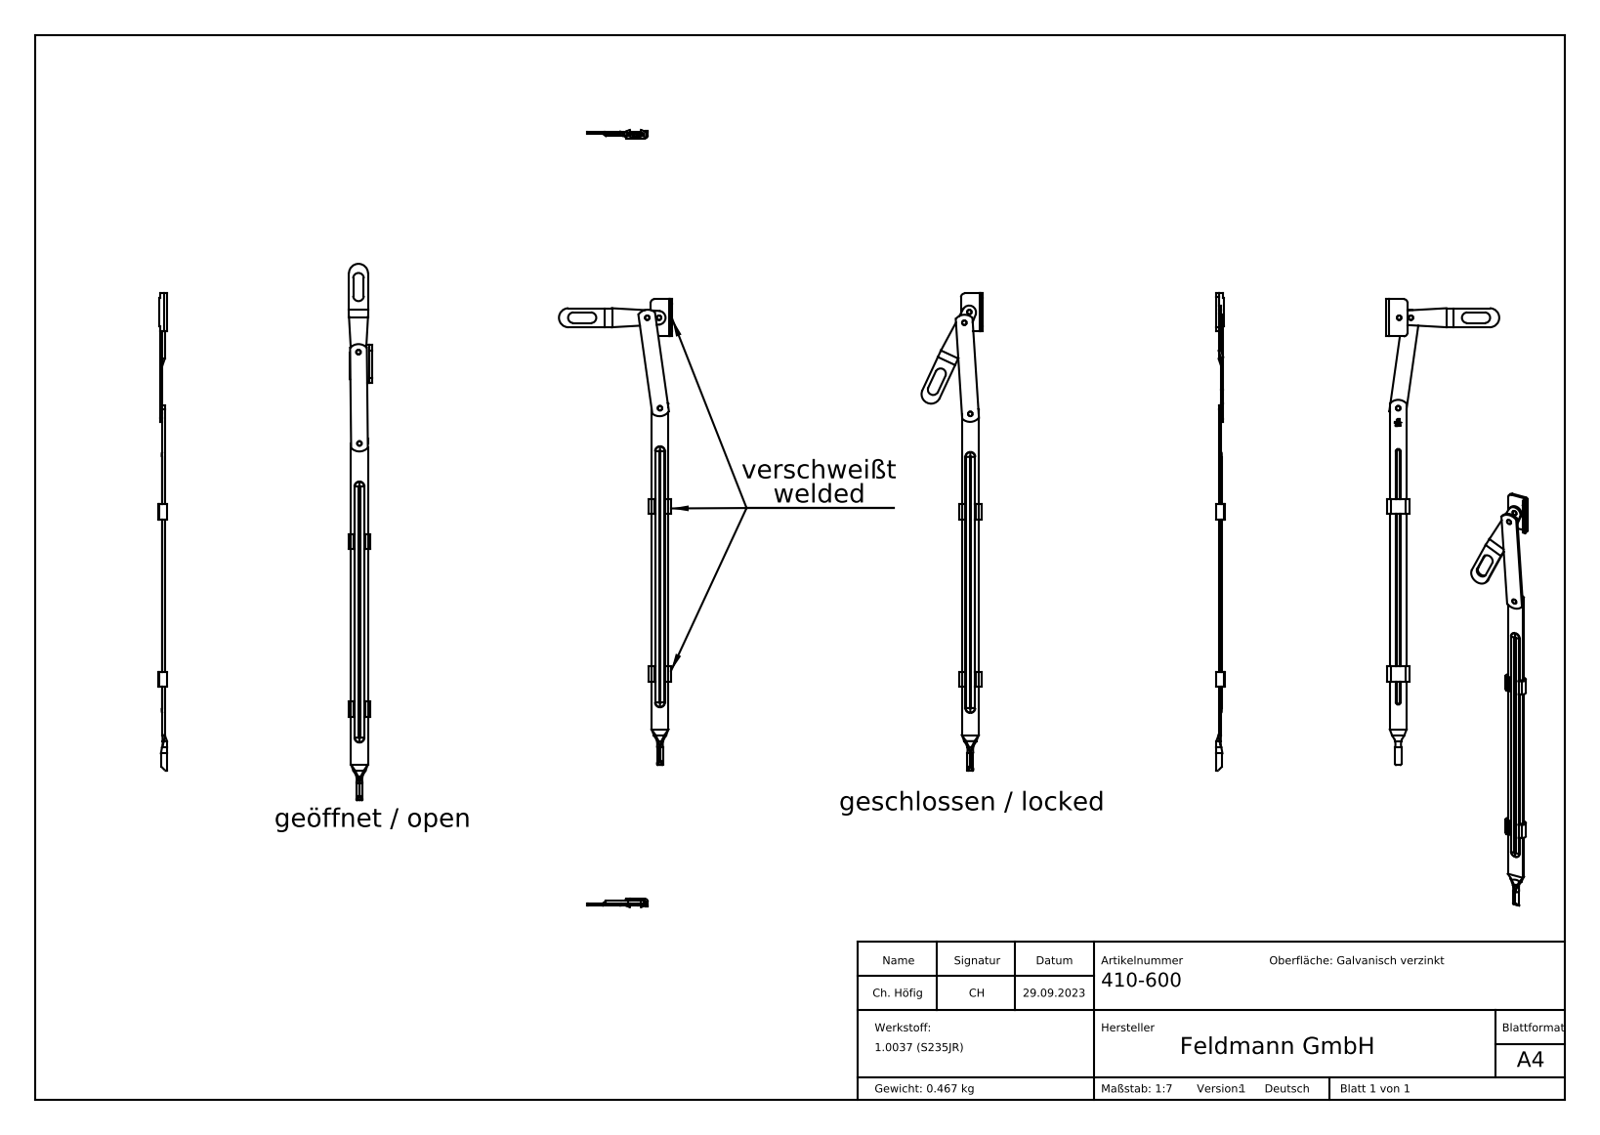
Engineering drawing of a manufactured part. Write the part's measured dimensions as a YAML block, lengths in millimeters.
part_name: "410-x00 Teil3_410-x00 Teil3; 410-x00 Teil2_410-x00 Teil2; 410-600; 410-x00 Teil5_410-x00 Teil5 (+3 more)"
step_written_by: "SolidWorks 2018 (CONFIG_CONTROL_DESIGN)"
units: millimeters
bodies: {solids: 9, faces: 362, planar: 191, cylindrical: 37, other: 134}
overall_size: [612.33, 149, 11]
volume: 59859
surface_area: 46394
round_holes:
  - {diameter: 6, count: 3}
  - {diameter: 4, count: 1}
round_bosses_or_shafts:
  - {diameter: 5.9, count: 3}
  - {diameter: 8, count: 1}
partial_cylinders:
  - {radius: 0.5, count: 6}
  - {radius: 5, count: 4}
  - {radius: 2, count: 2}
  - {radius: 7, count: 2}
  - {radius: 15, count: 2}
  - {radius: 1, count: 1}
  - {radius: 3, count: 1}
  - {radius: 4, count: 1}
face_to_face_distances: [3, 6, 4, 1, 2, 9, 22, 5, 7, 24.25]
hole_center_spacings: [15.5, 118.84, 120]
